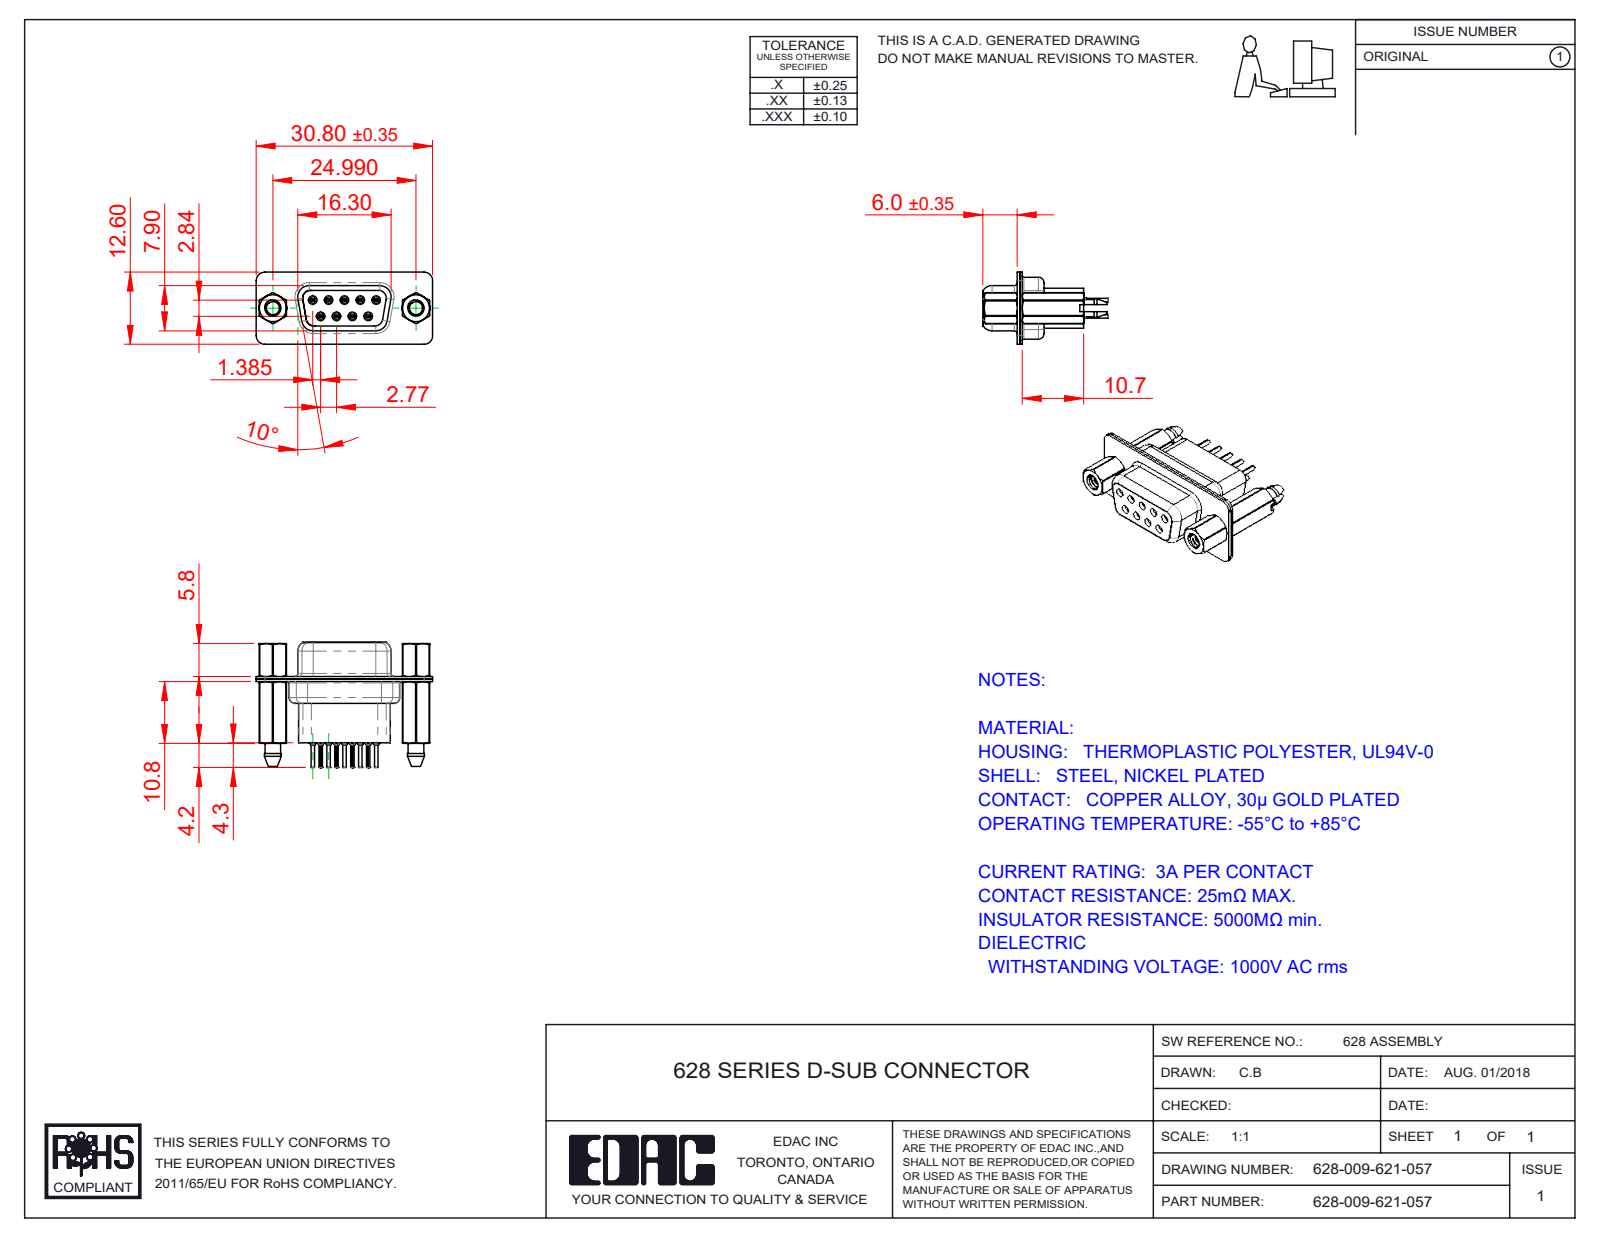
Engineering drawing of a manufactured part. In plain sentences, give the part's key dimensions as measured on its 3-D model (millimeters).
The part is named "628 Housing_09 HP; 628-009-621-057; 628 Contact Row 1_21H; 628 4-40 Hex Standoff (+4 more)". Its 3-D file was written by "SolidWorks 2020 (CONFIG_CONTROL_DESIGN)". It is 16 solids with 1626 faces: 400 planar, 574 cylindrical and 652 other. Overall it measures 30.8 by 21.9 by 12.6 millimeters. Its volume is 2 695 cubic millimeters and its surface area 6 399 square millimeters. Round holes: 9 of diameter 0.2, 9 of diameter 0.8, 9 of diameter 0.9, 9 of diameter 1.1, 9 of diameter 1.6, 5 of diameter 1.7, 2 of diameter 2.26, 2 of diameter 2.29, 2 of diameter 4, 2 of diameter 4.05, 2 of diameter 4.85. Round bosses or shafts: 9 of diameter 2, 9 of diameter 1.5, 9 of diameter 1.2, 9 of diameter 0.6, 2 of diameter 4.95, 2 of diameter 4.8, 2 of diameter 2.79. Partial cylindrical surfaces (rounded edges, fillets, slot ends): 19 of radius 1.5, 18 of radius 0.1, 12 of radius 2, 9 of radius 0.28, 6 of radius 1.35, 6 of radius 1.6, 4 of radius 0.25, 4 of radius 0.5. The main face-to-face distances are 0.45, 0.4, 0.9, 8.5, 4.76, 6.6, 1.9, 7, 1.4, 0.5. The hole center spacings are 3.16, 2.77, 5.54, 5.03, 5.04, 8.31, 7.48, 7.49.
